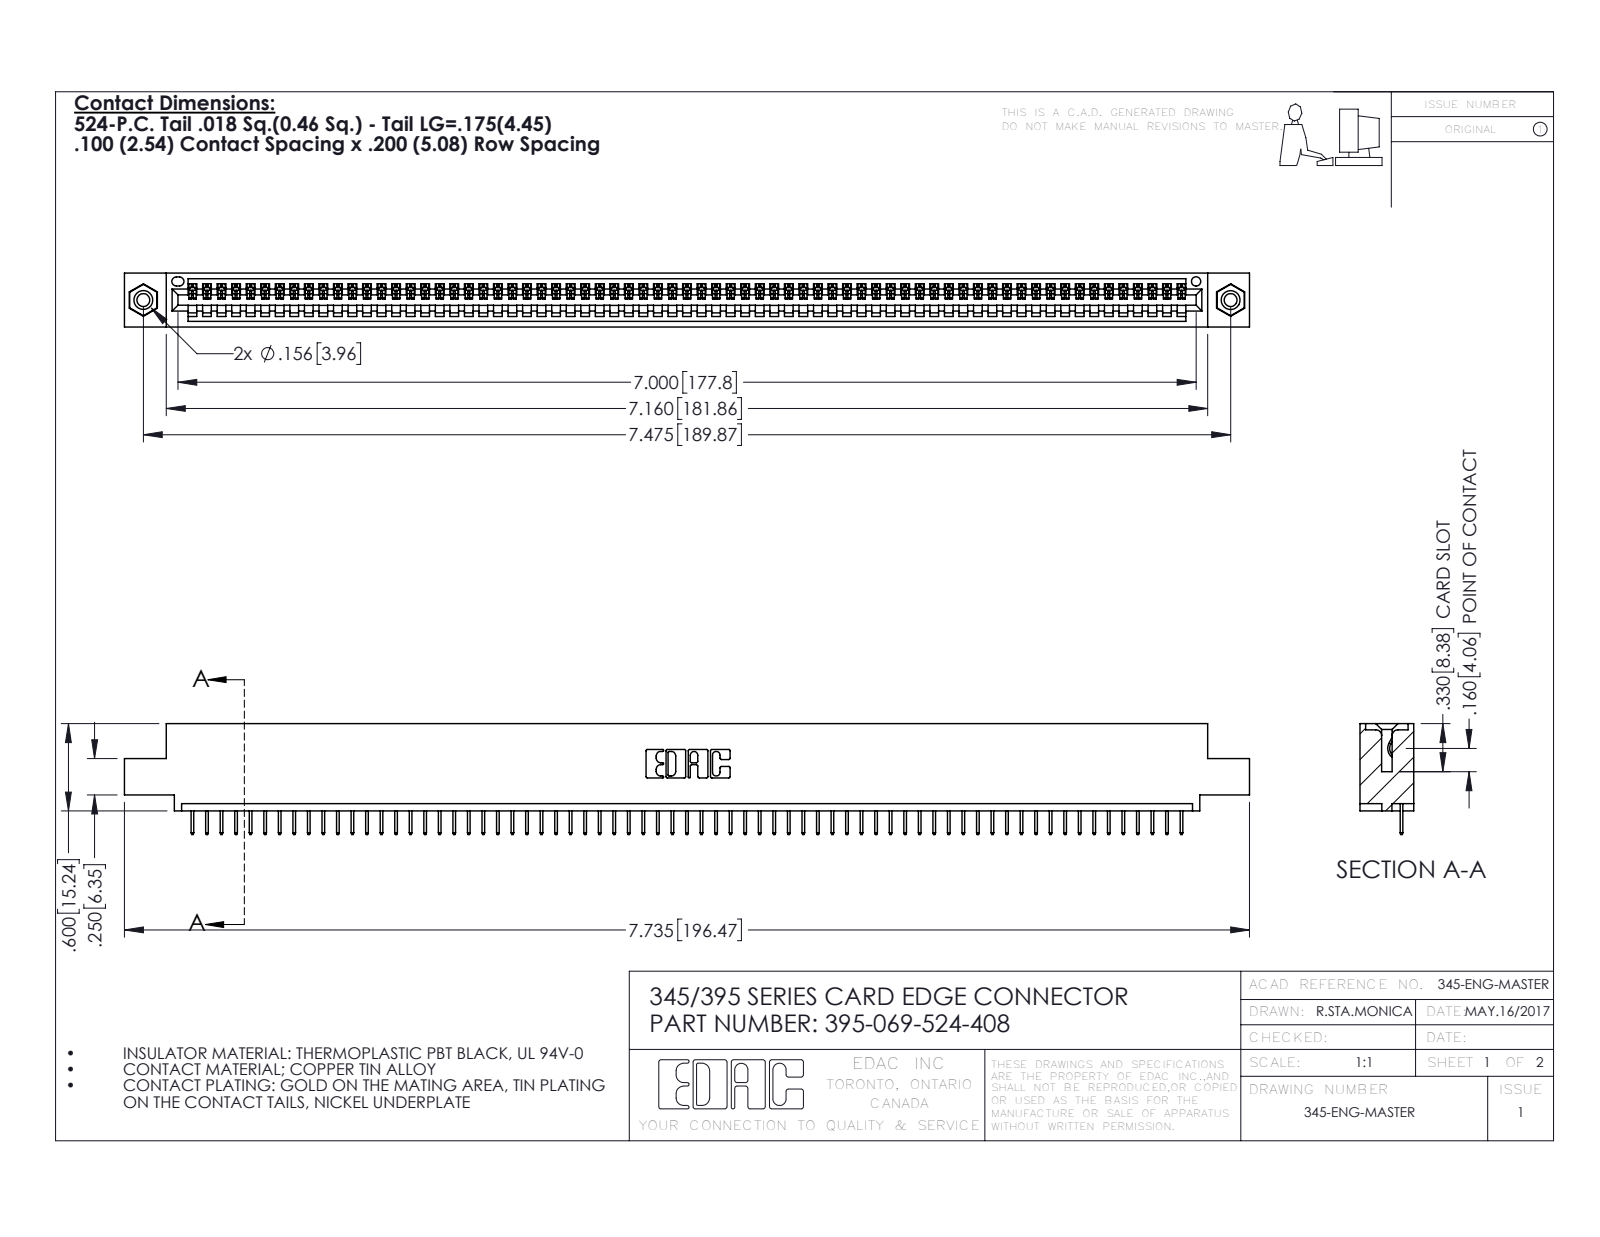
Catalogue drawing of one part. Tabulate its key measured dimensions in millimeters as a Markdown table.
| quantity | value |
| --- | --- |
| part name | 395-069-524-408; 345-292-001_345-293-124; 345 Part_0.110 Offset - 0.156 Dia-TI; 345-250-001_345-250-003-102 |
| STEP written by | SolidWorks 2016 (CONFIG_CONTROL_DESIGN) |
| units | millimeters |
| bodies | 72 solids, 4468 faces (3290 planar, 1162 cylindrical, 16 other) |
| overall size | 196.5 × 19.4 × 9.4 |
| volume | 18 530 mm³ |
| surface area | 24 220 mm² |
| round holes (diameter × count) | 2.3 × 2, 3.2 × 2, 4 × 2, 1.6 × 1 |
| round bosses / shafts (diameter × count) | 3.9 × 2 |
| partial cylindrical surfaces (radius × count) | 0.2 × 138, 0.3 × 22, 0.2 × 6, 0.8 × 6, 0.7 × 3, 0.8 × 2, 1 × 2, 0.4 × 1 |
| main face-to-face distances | 1.8, 7.6, 9.4, 5.1, 2.5, 6.9, 0.6, 5.7, 1.8, 3.8 |
| hole center spacings | 6.9, 183.9, 189.9 |
